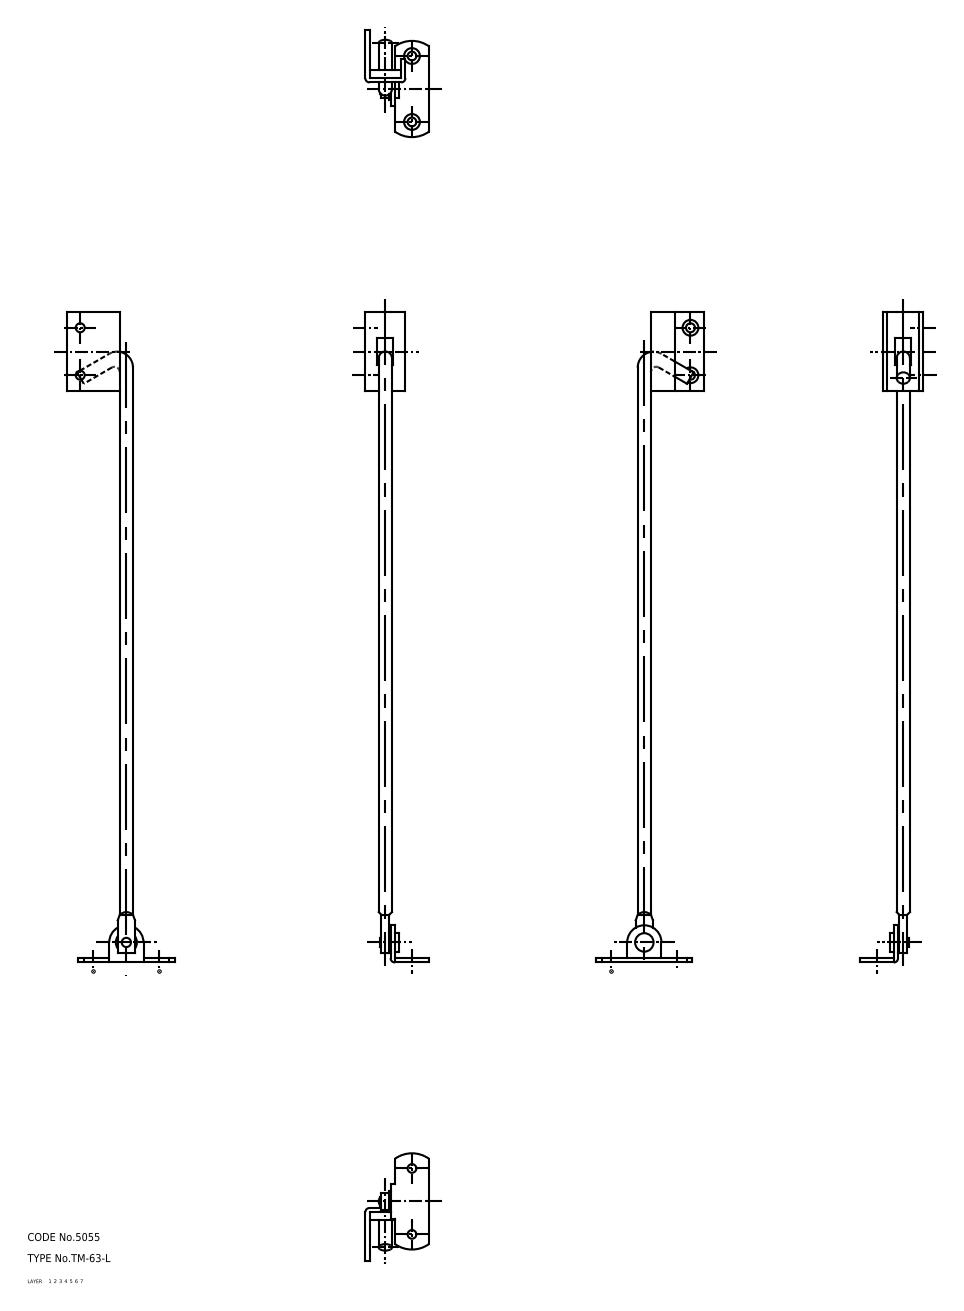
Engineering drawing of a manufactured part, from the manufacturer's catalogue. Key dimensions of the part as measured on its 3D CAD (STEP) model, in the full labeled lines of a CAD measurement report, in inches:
Part name (STEP PRODUCT): washer; stopper; rivet; cushion (+3 more)
STEP written by: CADfix (AUTOMOTIVE_DESIGN)
Units: inches
Bodies: 6 solids, 91 faces (0 planar, 0 cylindrical, 91 other)
Overall size (bounding box): 9.613 × 1.604 × 0.953
Volume: 0.516 in³ · Surface area: 14.05 in²
